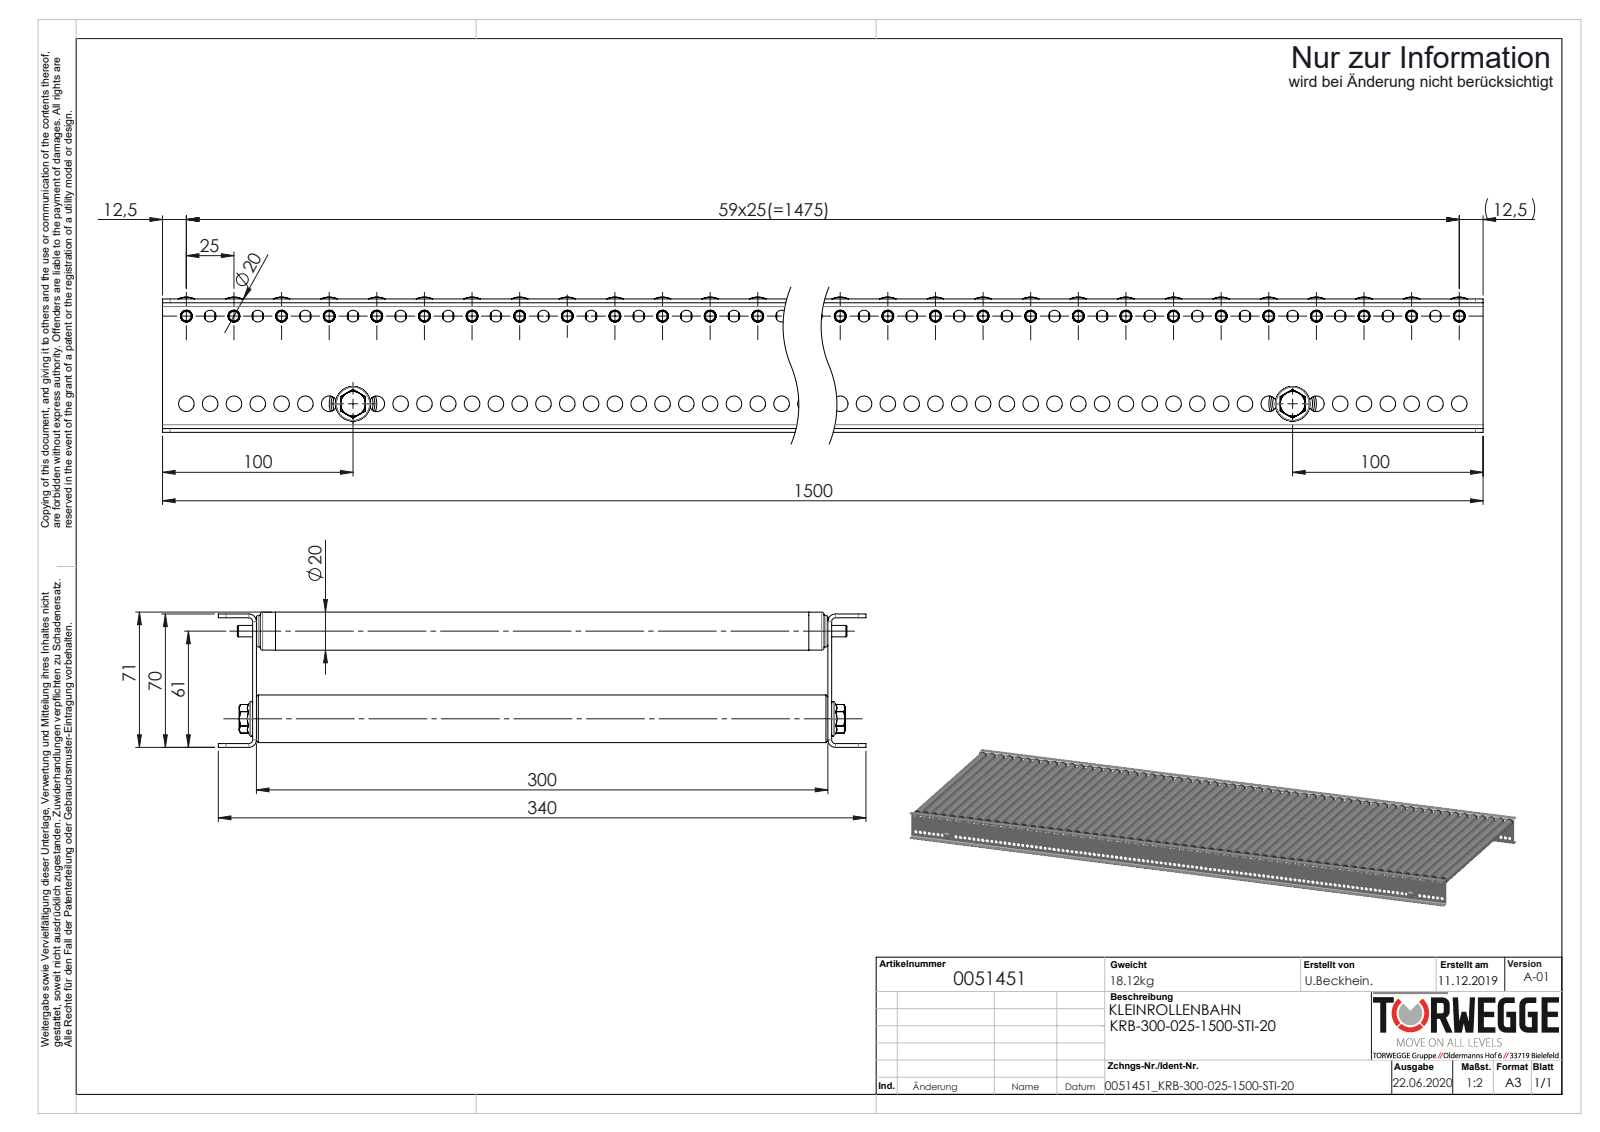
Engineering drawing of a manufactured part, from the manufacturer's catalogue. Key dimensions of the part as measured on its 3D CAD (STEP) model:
Part name (STEP PRODUCT): 0051451; S100994_Sperrzahnschraube_M08x16-8.8-A2K; 0039777_Achse-Ø06-FA-KFG_L=320 fr D20; S100992_Typ-KUT50-20x1-6 (+4 more)
STEP written by: SolidWorks 2020 (AUTOMOTIVE_DESIGN)
Units: millimetres
Bodies: 132 solids, 11792 faces (3840 planar, 4488 cylindrical, 3464 other)
Overall size (bounding box): 1500 × 340 × 71
Volume: 2 241 000 mm³ · Surface area: 3 475 000 mm²
Round holes (diameter × count): ⌀6.2 ×119, ⌀8.2 ×119, ⌀6.1 ×60, ⌀14.2 ×60, ⌀17.2 ×60, ⌀18 ×60, ⌀6.8 ×2, ⌀21 ×2
Round bosses / shafts (diameter × count): ⌀20 ×60, ⌀19.9 ×60, ⌀18.1 ×60, ⌀17.8 ×60, ⌀16.5 ×60, ⌀6 ×60, ⌀25 ×2, ⌀8 ×2
Partial cylindrical surfaces — rounded edges, fillets, slot ends (radius × count): R4.05 ×60, R4 ×8, R2 ×4
Main face-to-face distances: 2, 302, 68, 300, 304, 70, 66, 292, 18, 30
Hole centre spacings: 12.5, 25, 37.5, 50, 62.5, 75, 87.5, 100
